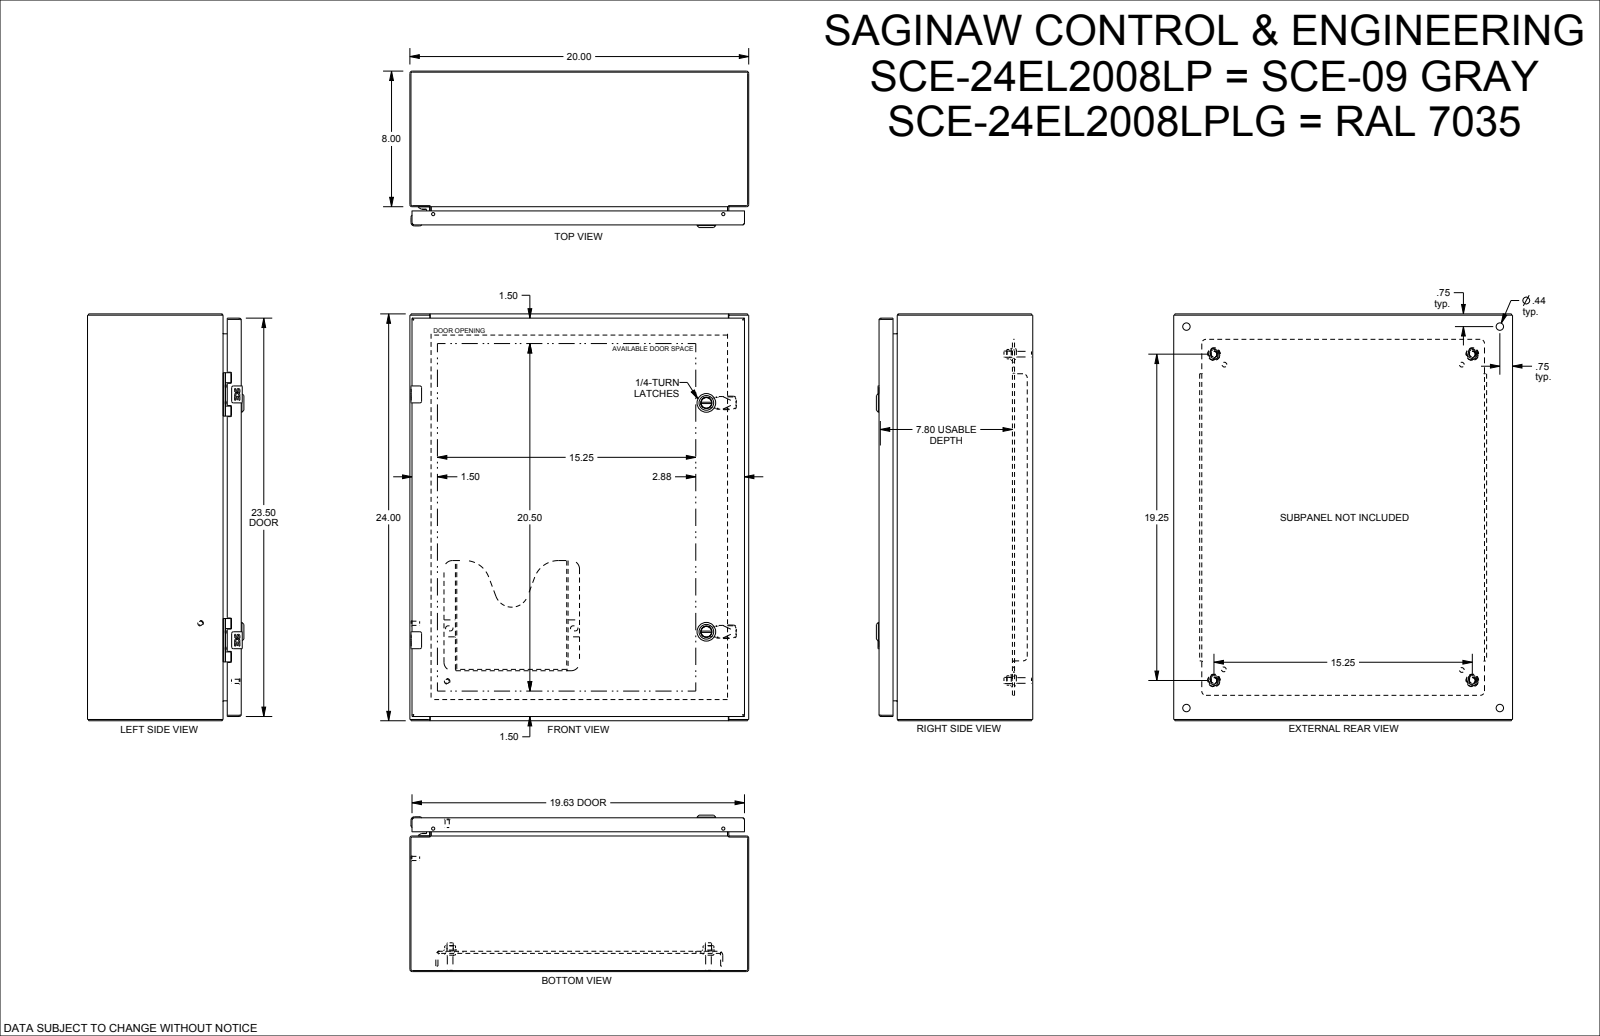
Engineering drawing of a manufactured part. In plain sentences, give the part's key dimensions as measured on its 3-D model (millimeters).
The part is named "SCE-24EL2008LP". Its 3-D file was written by "SolidWorks 2021 (AUTOMOTIVE_DESIGN)". It is 47 solids with 2911 faces: 1099 planar, 892 cylindrical and 920 other. Overall it measures 609.6 by 508 by 234.4 millimeters. Its volume is 3 271 000 cubic millimeters and its surface area 3 112 000 square millimeters. Round holes: 4 of diameter 4.4, 4 of diameter 5.2, 4 of diameter 6.2, 4 of diameter 6.8, 4 of diameter 7.1, 4 of diameter 9.3, 4 of diameter 9.5, 4 of diameter 11.1, 4 of diameter 12.7, 2 of diameter 1, 2 of diameter 4.8, 2 of diameter 5. Round bosses or shafts: 6 of diameter 4.3, 4 of diameter 9.3, 4 of diameter 8.4, 4 of diameter 6.4, 4 of diameter 6.3, 4 of diameter 6.1, 3 of diameter 5, 2 of diameter 28. Partial cylindrical surfaces (rounded edges, fillets, slot ends): 56 of radius 0.3, 28 of radius 0.3, 24 of radius 0.4, 20 of radius 0.5, 17 of radius 1, 13 of radius 1.5, 12 of radius 0.6, 12 of radius 0.7. The main face-to-face distances are 1.9, 1.5, 230.5, 228.5, 228.9, 227, 506.1, 25.4, 3.2, 30.5. The hole center spacings are 25, 368.3, 0.5, 12.5, 12.5, 22.2, 58.4, 114.1.
